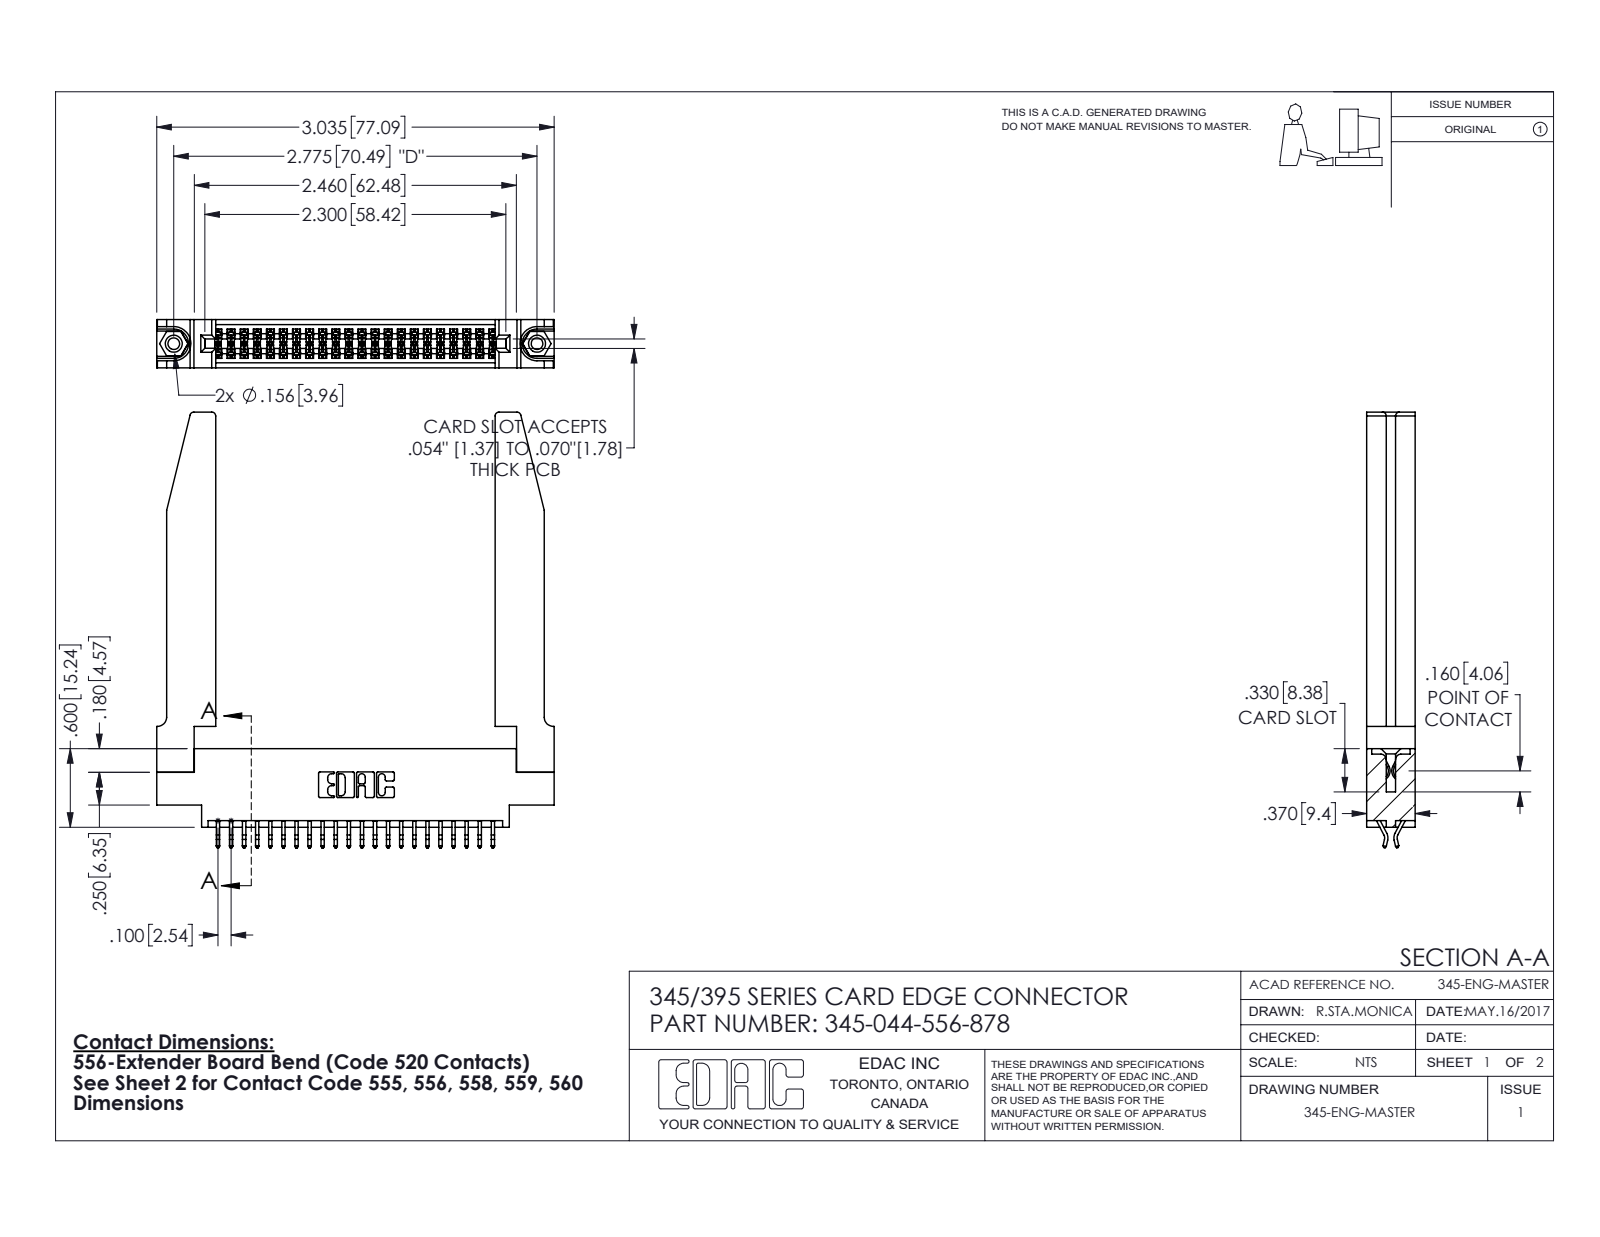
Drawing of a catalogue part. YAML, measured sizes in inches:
part_name: "345 Part_0.170 Offset - 0.156 Dia-TH; 345-220-078_345-220-078; 345-044-556-878; 345-250-001_345-250-001-102 (+1 more)"
step_written_by: "SolidWorks 2016 (CONFIG_CONTROL_DESIGN)"
units: inches
bodies: {solids: 49, faces: 2828, planar: 1854, cylindrical: 922, other: 52}
overall_size: [3.327, 3.036, 0.37]
volume: 0.913
surface_area: 26.64
round_holes:
  - {diameter: 0.089, count: 2}
  - {diameter: 0.125, count: 2}
  - {diameter: 0.156, count: 2}
  - {diameter: 0.064, count: 1}
round_bosses_or_shafts:
  - {diameter: 0.155, count: 2}
partial_cylinders:
  - {radius: 0.006, count: 66}
  - {radius: 0.01, count: 22}
  - {radius: 0.03, count: 8}
  - {radius: 0.007, count: 6}
  - {radius: 0.031, count: 6}
  - {radius: 0.026, count: 3}
  - {radius: 0.01, count: 2}
  - {radius: 0.014, count: 2}
face_to_face_distances: [0.37, 0.072, 0.298, 0.025, 0.098, 0.272, 0.2, 0.225, 0.148, 0.15]
hole_center_spacings: [0.27, 2.541, 2.775]
